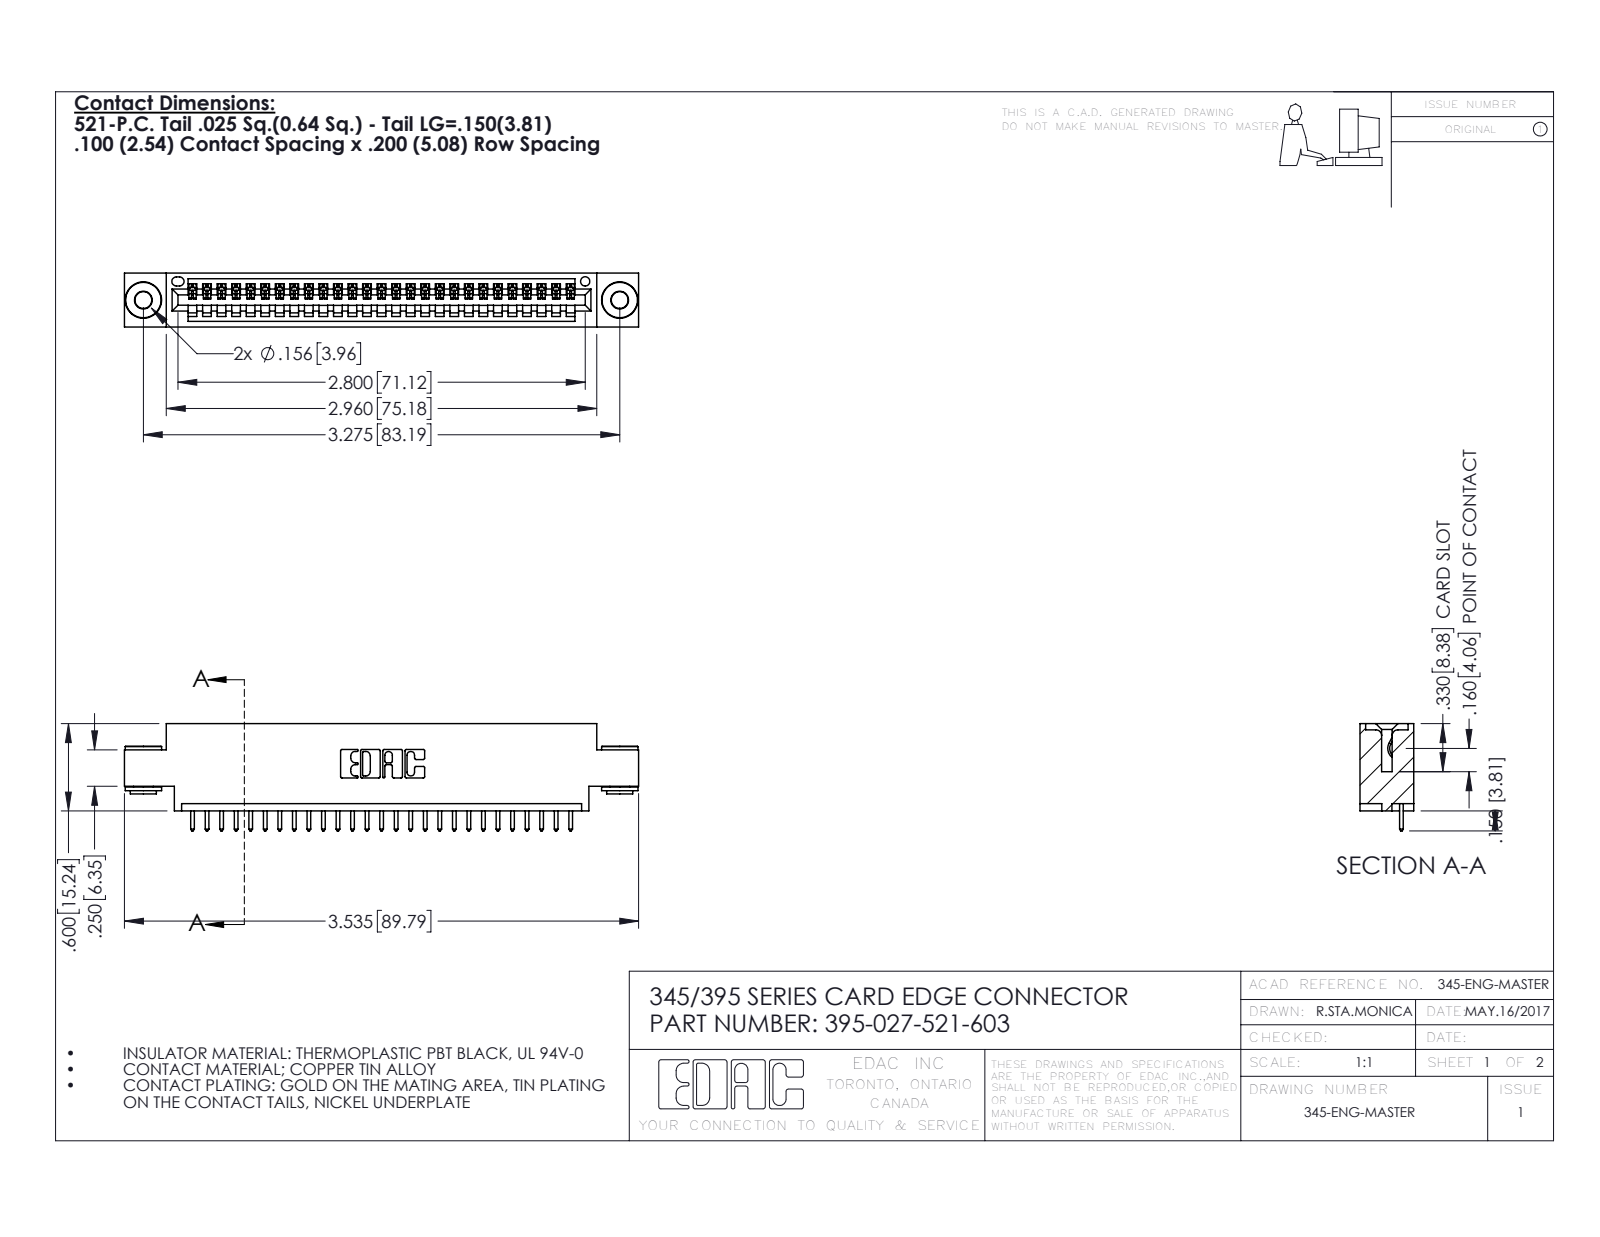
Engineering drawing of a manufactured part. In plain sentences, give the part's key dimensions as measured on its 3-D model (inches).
The part is named "345-250-002_345-250-002-102; 395-027-521-603; 345-292-001_345-293-121; 345 Part_0.170 Offset - 0.156 Dia-TH". Its 3-D file was written by "SolidWorks 2016 (CONFIG_CONTROL_DESIGN)". It is 30 solids with 1734 faces: 1174 planar, 552 cylindrical and 8 other. Overall it measures 3.535 by 0.737 by 0.37 inches. Its volume is 0.503 cubic inches and its surface area 16.71 square inches. Round holes: 2 of diameter 0.116, 2 of diameter 0.156, 1 of diameter 0.064. Round bosses or shafts: 2 of diameter 0.25, 2 of diameter 0.18, 2 of diameter 0.136. Partial cylindrical surfaces (rounded edges, fillets, slot ends): 54 of radius 0.006, 54 of radius 0.01, 22 of radius 0.01, 6 of radius 0.007, 6 of radius 0.031, 3 of radius 0.026, 2 of radius 0.031, 2 of radius 0.04. The main face-to-face distances are 0.072, 0.298, 0.37, 0.2, 0.098, 0.272, 0.025, 0.225, 0.175, 0.1. The hole center spacings are 0.27, 3.04, 3.275.
